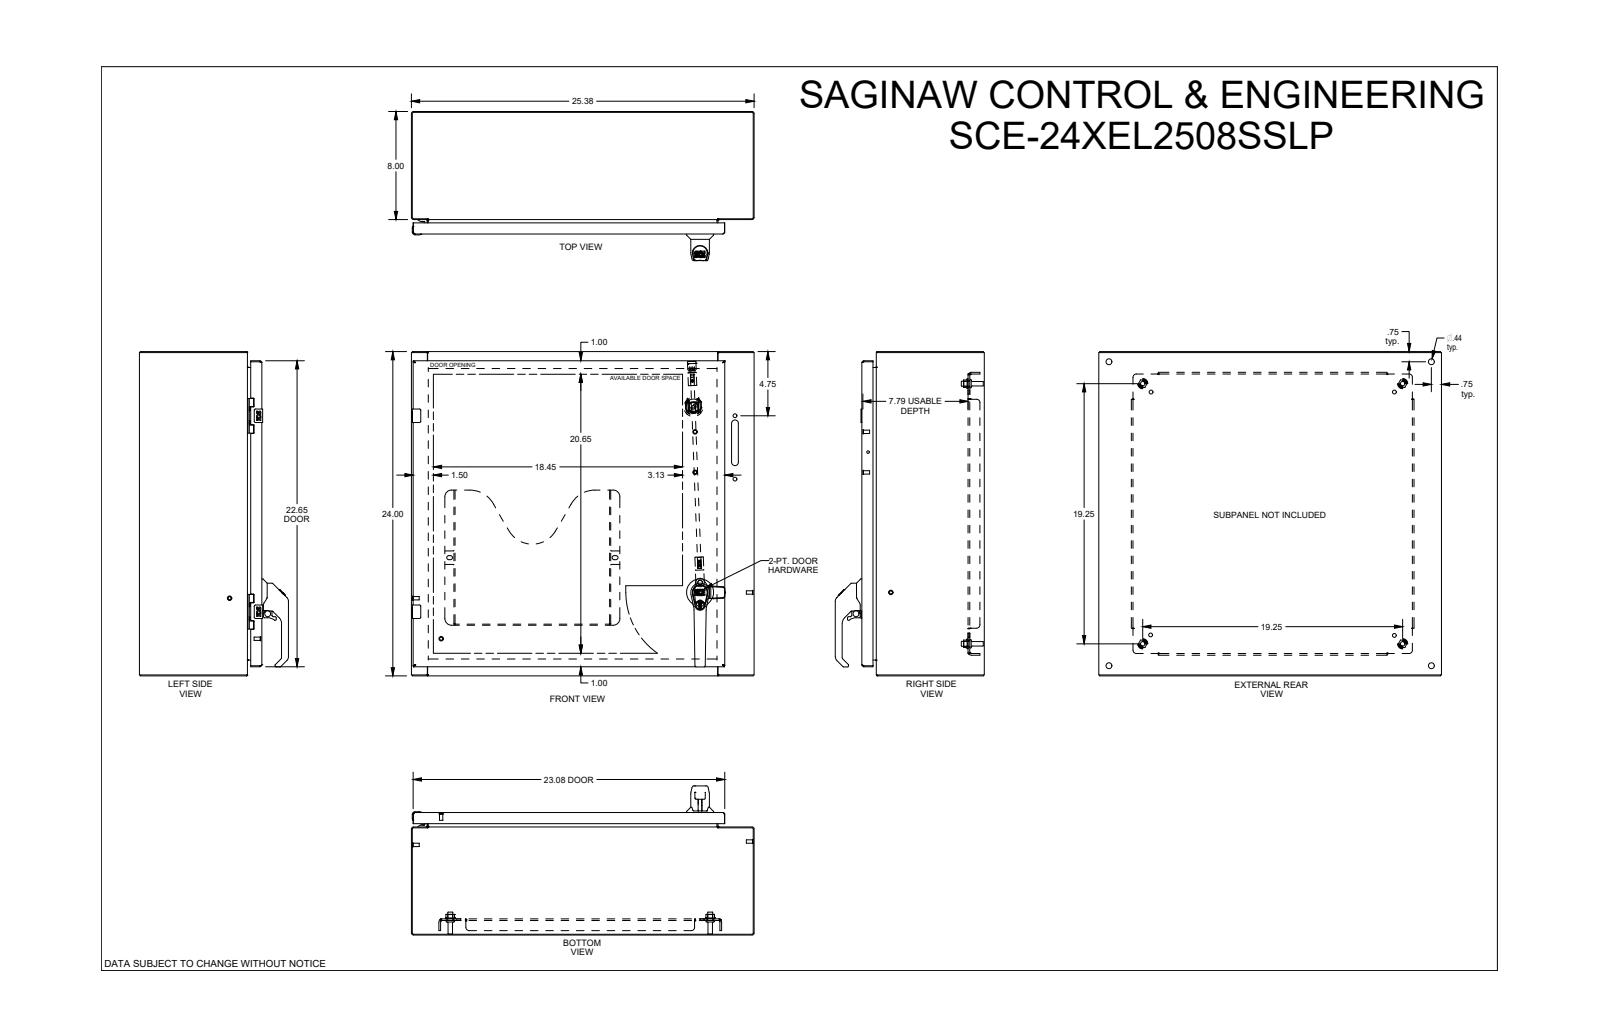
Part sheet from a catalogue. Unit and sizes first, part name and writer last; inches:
Units: inches
Overall size (bounding box): 25.375 × 24 × 11.036
Round holes (diameter × count): ⌀0.281 ×6, ⌀0.266 ×5, ⌀0.172 ×4, ⌀0.205 ×4, ⌀0.244 ×4, ⌀0.367 ×4, ⌀0.375 ×4, ⌀0.437 ×4, ⌀0.5 ×4, ⌀0.25 ×3, ⌀0.25 ×3, ⌀0.138 ×2
Round bosses / shafts (diameter × count): ⌀0.248 ×8, ⌀0.17 ×6, ⌀0.366 ×4, ⌀0.332 ×4, ⌀0.25 ×4, ⌀0.563 ×3, ⌀0.196 ×3, ⌀0.341 ×2
Partial cylindrical surfaces — rounded edges, fillets, slot ends (radius × count): R0.03 ×69, R0.015 ×58, R0.01 ×36, R0.02 ×36, R0.02 ×34, R0.04 ×31, R0.039 ×30, R0.005 ×26
Main face-to-face distances: 0.075, 8.993, 8.918, 1.125, 1.2, 7.868, 7.793, 9.068, 0.125, 7.918
Hole centre spacings: 14.5, 0.985, 0.02, 4.493, 0.472, 0.725, 0.854, 0.866
Volume: 261.2 in³ · Surface area: 5 987 in²
Bodies: 67 solids, 4628 faces (1743 planar, 1218 cylindrical, 1667 other)
Part name (STEP PRODUCT): SCE-24XEL2508SSLP
STEP written by: SolidWorks 2019 (CONFIG_CONTROL_DESIGN)
